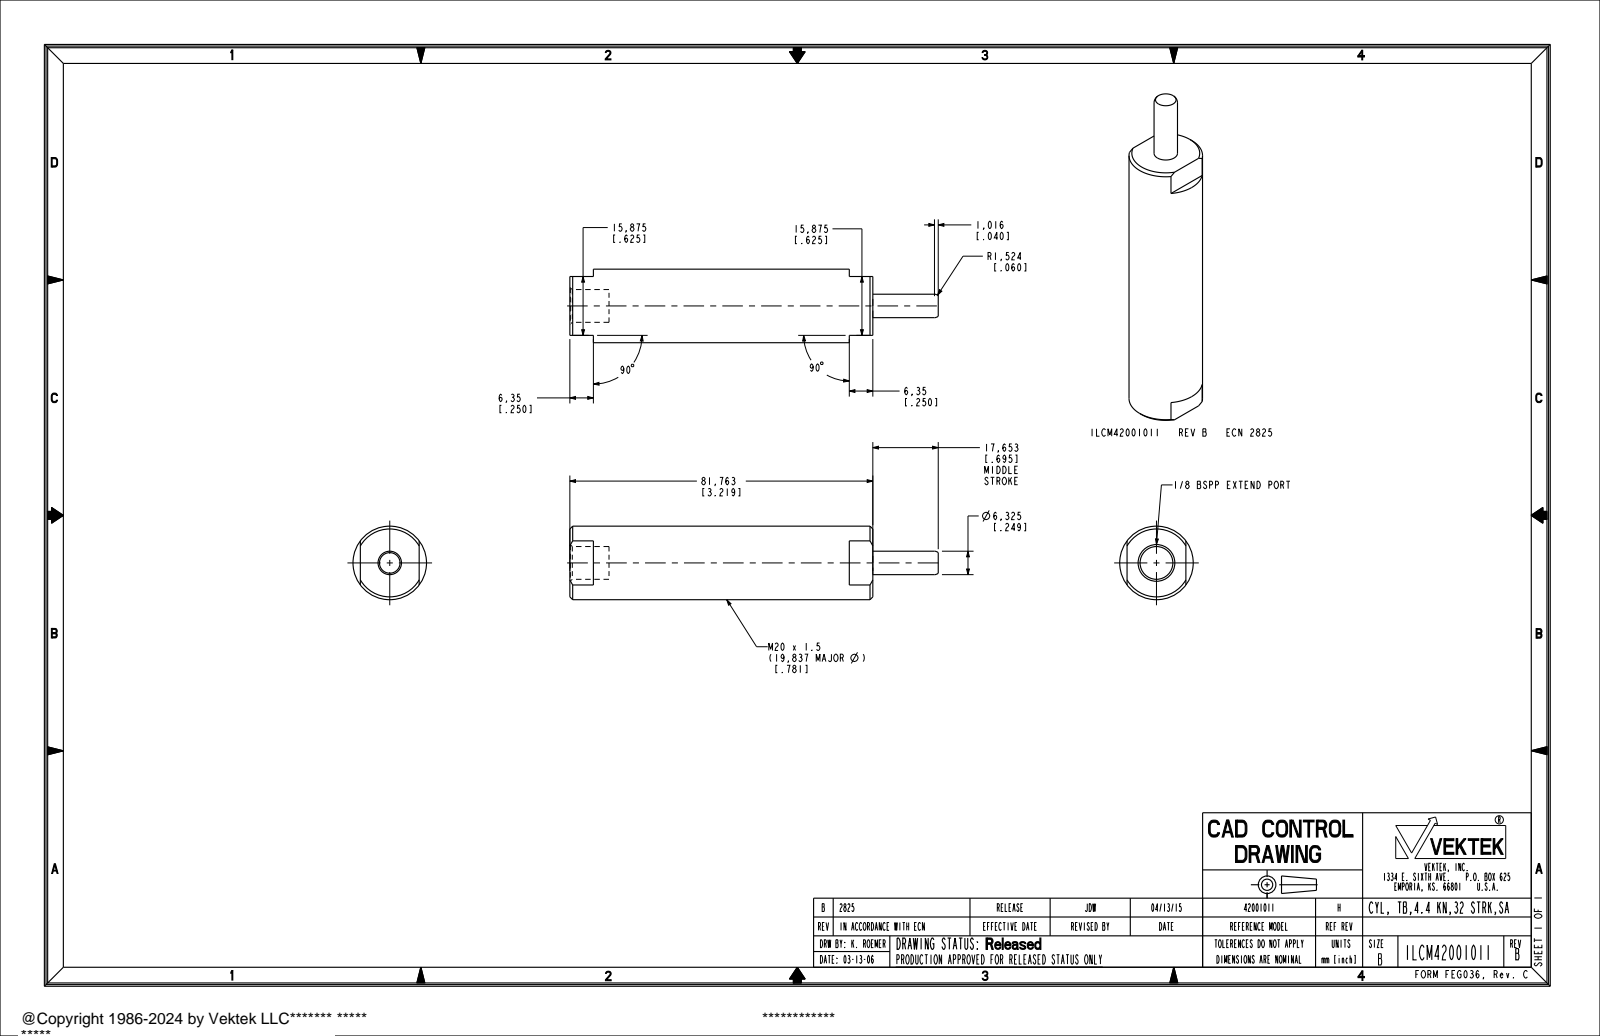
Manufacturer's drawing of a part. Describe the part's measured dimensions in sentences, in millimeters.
The part is named "ILCM42001011". Its 3-D file was written by "PRO/ENGINEER BY PARAMETRIC TECHNOLOGY CORPORATION, 2013320 (AUTOMOTIVE_DESIGN)". It is 1 solid with 28 faces: 12 planar, 8 cylindrical and 8 other. Overall it measures 99.42 by 19.84 by 19.84 millimeters. Its volume is 24 738 cubic millimeters and its surface area 6 285 square millimeters. Round holes: 1 of diameter 8.84, 1 of diameter 9.91. Round bosses or shafts: 1 of diameter 19.84, 1 of diameter 6.33. The main face-to-face distances are 81.76, 15.88, 6.35, 75.41, 10.57, 71.19, 4.22, 69.06, 64.84, 99.42.
